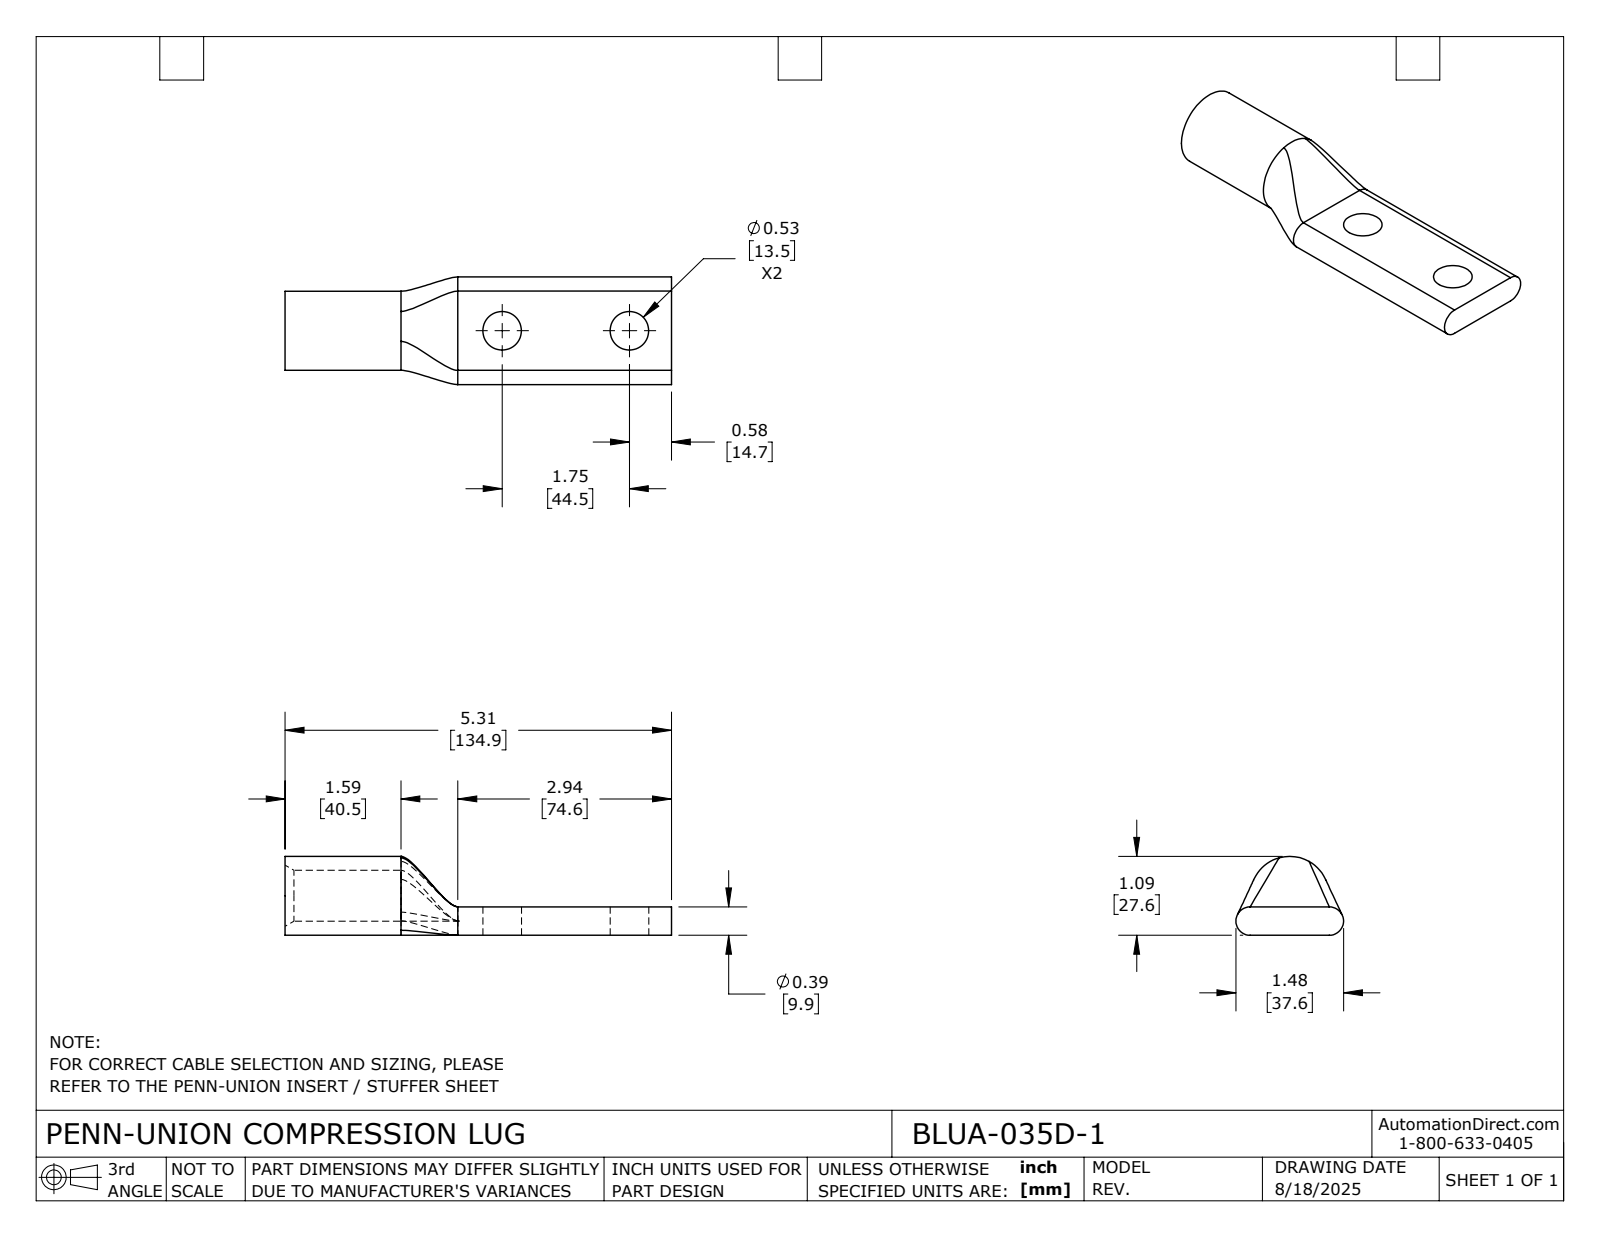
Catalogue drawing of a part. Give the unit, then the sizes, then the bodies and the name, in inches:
Units: inches
Overall size (bounding box): 5.312 × 1.48 × 1.085
Round holes (diameter × count): ⌀0.531 ×2, ⌀0.7 ×1
Round bosses / shafts (diameter × count): ⌀1.085 ×1
Partial cylindrical surfaces — rounded edges, fillets, slot ends (radius × count): R0.196 ×2
Main face-to-face distances: 0.391, 5.312, 2.375, 2.937
Hole centre spacings: 1.75
Volume: 2.701 in³ · Surface area: 25.18 in²
Bodies: 1 solid, 26 faces (5 planar, 11 cylindrical, 10 other)
Part name (STEP PRODUCT): BLUA-035D-1
STEP written by: SolidWorks 2024 (CONFIG_CONTROL_DESIGN)
